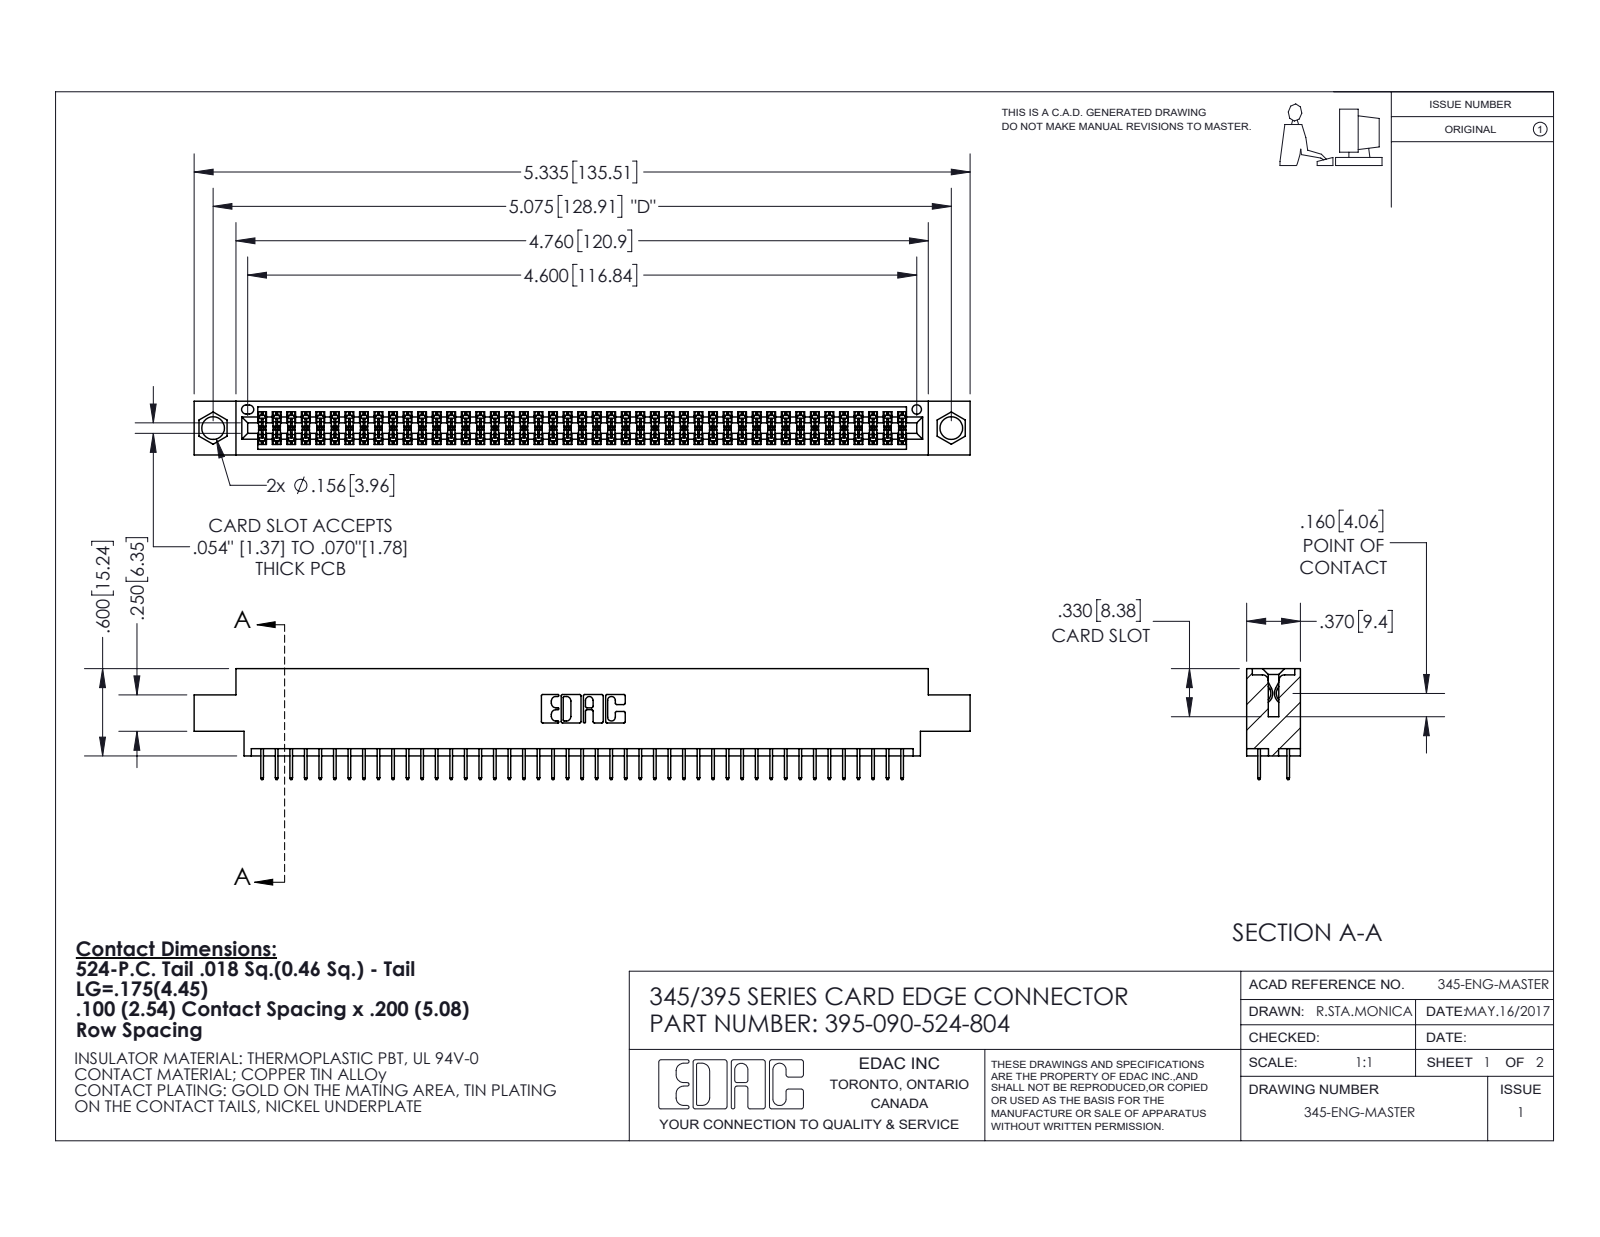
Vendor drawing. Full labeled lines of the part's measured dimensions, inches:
Part name (STEP PRODUCT): 395-090-524-804; 345-292-001_345-293-124; 345 Part_0.170 Offset - 0.156 Dia-TI
STEP written by: SolidWorks 2020 (CONFIG_CONTROL_DESIGN)
Units: inches
Bodies: 91 solids, 5004 faces (3608 planar, 1396 cylindrical, 0 other)
Overall size (bounding box): 5.335 × 0.762 × 0.37
Volume: 0.783 in³ · Surface area: 28.93 in²
Round holes (diameter × count): ⌀0.156 ×2, ⌀0.064 ×1
Partial cylindrical surfaces — rounded edges, fillets, slot ends (radius × count): R0.006 ×135, R0.01 ×22, R0.007 ×6, R0.031 ×6, R0.026 ×3, R0.014 ×2, R0.019 ×2, R0.022 ×2
Main face-to-face distances: 0.072, 0.298, 0.37, 0.2, 0.098, 0.272, 0.025, 0.225, 0.175, 0.072
Hole centre spacings: 0.27, 4.839, 5.075
